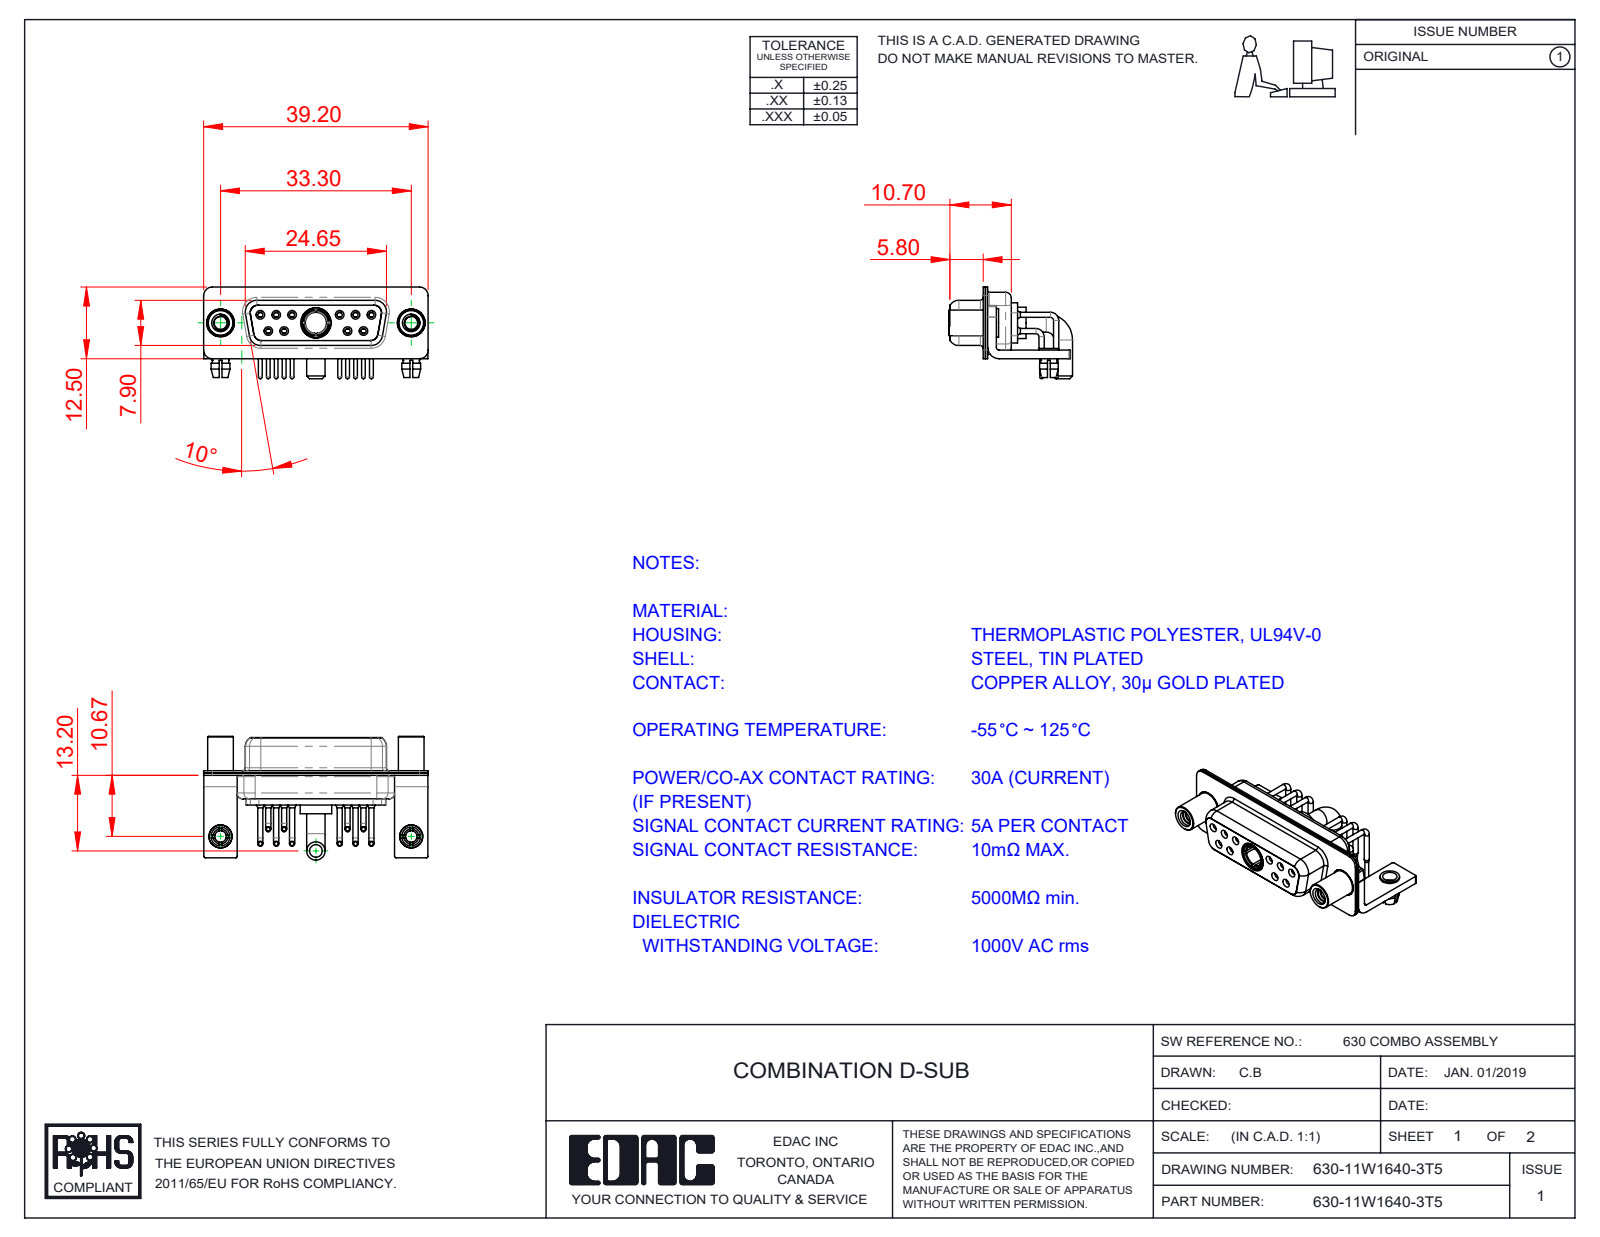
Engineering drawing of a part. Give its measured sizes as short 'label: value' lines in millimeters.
name: Power Socket_30A RA; 630Combo Shell Front_15 Contacts; 630Combo Contact Row 2; 630Combo Threaded Standoff_5 (+6 more)
written by: SolidWorks 2020 (CONFIG_CONTROL_DESIGN)
unit: mm
bodies: 21 solids, 1067 faces (316 planar, 484 cylindrical, 267 other)
size: 39.2 × 21.6 × 16
volume: 3 107 mm³; area: 7 415 mm²
holes: 12× ⌀2, 10× ⌀0.9, 10× ⌀1.1, 10× ⌀1.5, 6× ⌀1.7, 4× ⌀1.6, 3× ⌀4.85, 2× ⌀2.26, 2× ⌀2.5, 2× ⌀3.2, 2× ⌀4, 2× ⌀4.05
bosses: 10× ⌀0.9, 10× ⌀0.65, 6× ⌀1.6, 2× ⌀5, 2× ⌀4.95, 2× ⌀4.8, 2× ⌀4.5, 2× ⌀4
rounds: 16× R0.25, 16× R1.5, 13× R2, 12× R1.35, 8× R1.6, 5× R0.5, 4× R0.6, 4× R0.65
face distances: 0.4, 0.8, 0.45, 1.4, 8.45, 1.5, 1.8, 8.9, 6.2, 2.3
hole spacings: 3.16, 2.77, 13.85, 11.08, 16.62, 5.03, 5.04, 5.54
